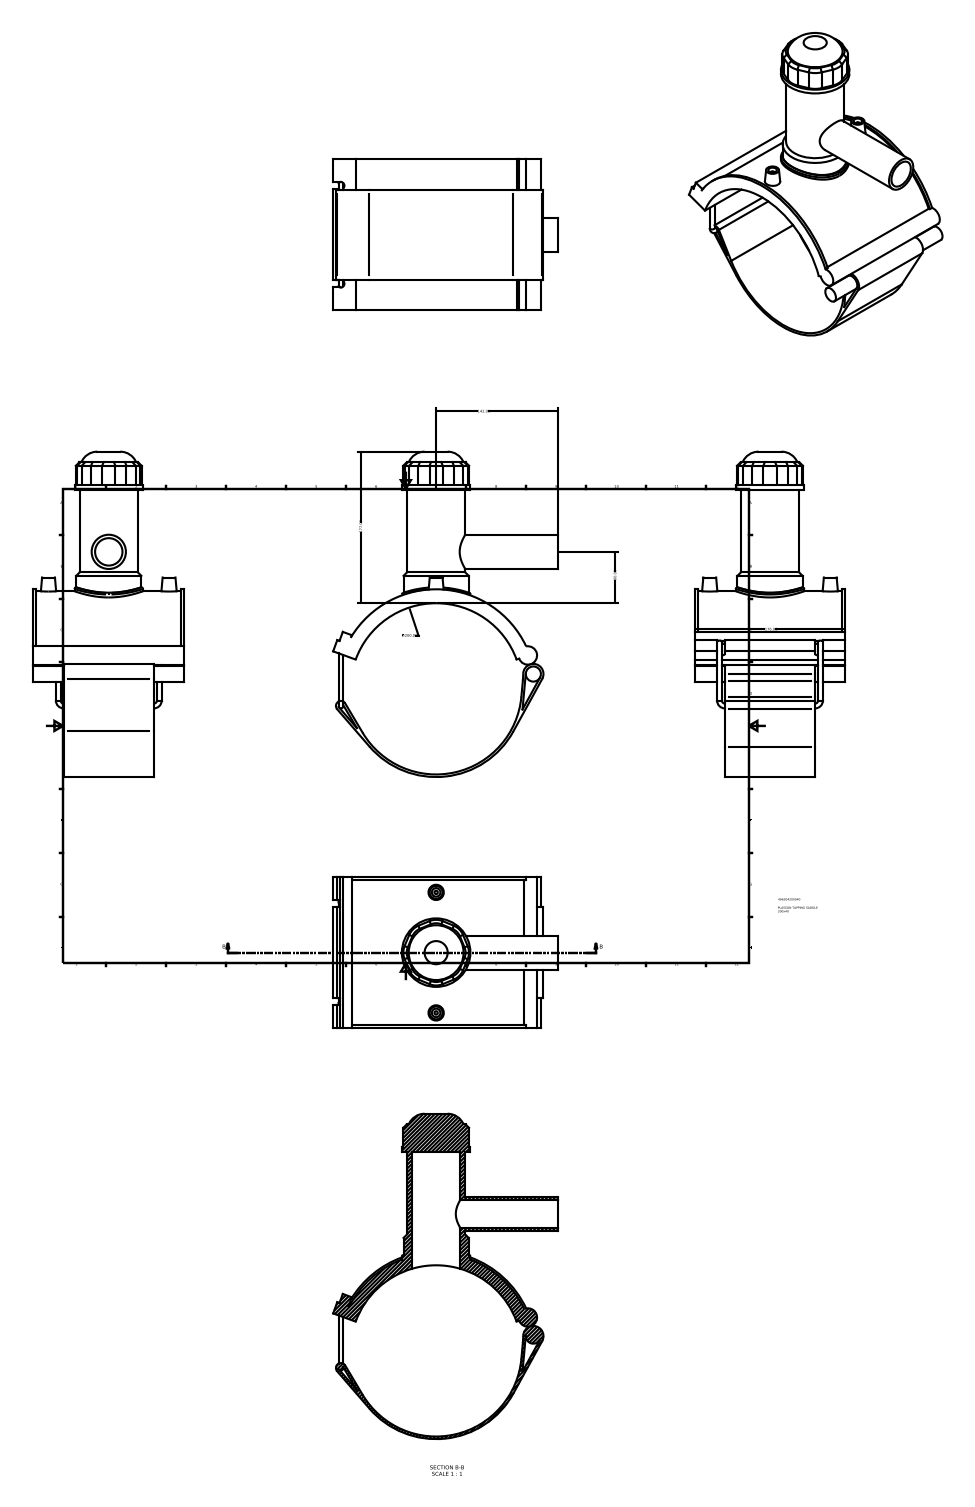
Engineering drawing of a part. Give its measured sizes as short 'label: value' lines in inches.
name: 496304200040
written by: Autodesk Inventor 2015 (AUTOMOTIVE_DESIGN)
unit: in
bodies: 1 solid, 121 faces (68 planar, 38 cylindrical, 15 other)
size: 14.961 × 10.326 × 6.929
volume: 79.33 in³; area: 485.1 in²
holes: 2× ⌀0.394, 1× ⌀1.26, 1× ⌀2.205
bosses: 2× ⌀0.22, 2× ⌀0.157, 1× ⌀3.15, 1× ⌀2.992, 1× ⌀2.677, 1× ⌀1.575, 1× ⌀0.696
rounds: 8× R0.787, 2× R0.165, 2× R3.937, 1× R0.11, 1× R0.228, 1× R0.424, 1× R0.467, 1× R4.055
face distances: 0.118, 6.929, 0.119, 1.386, 5.543, 0.441, 0.551, 0.106, 0.993, 0.11
hole spacings: 2.772, 5.543
